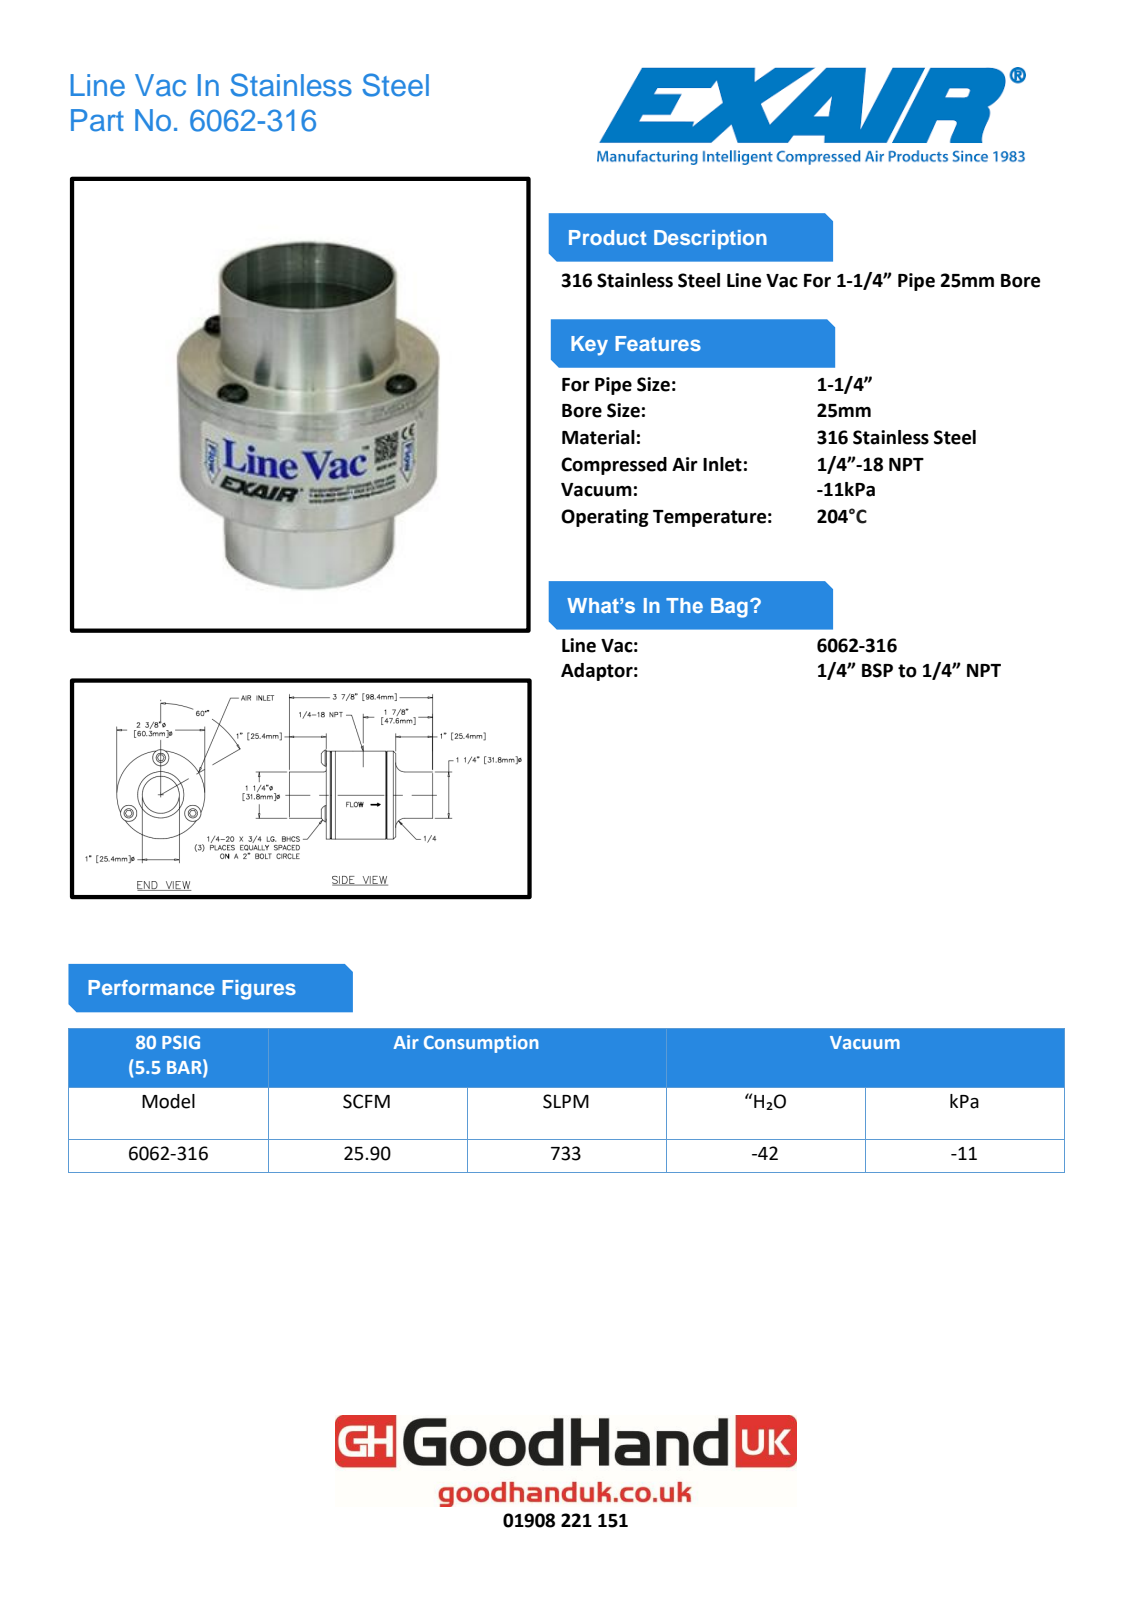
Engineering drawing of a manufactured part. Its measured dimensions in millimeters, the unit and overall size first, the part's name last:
Units: millimetres
Overall size (bounding box): 98.4 × 61.1 × 60.3
Round holes (diameter × count): ⌀5.2 ×3, ⌀6.4 ×3, ⌀7.1 ×3, ⌀11.1 ×1, ⌀25.4 ×1, ⌀41.9 ×1
Round bosses / shafts (diameter × count): ⌀60.3 ×1, ⌀60.3 ×1, ⌀31.8 ×1
Main face-to-face distances: 6.4, 9.5, 3.2, 47.6, 41.3, 38.1, 25.4, 73, 66.7, 63.5
Hole centre spacings: 44, 25.4, 25.4
Volume: 122 500 mm³ · Surface area: 35 650 mm²
Bodies: 5 solids, 84 faces (12 planar, 18 cylindrical, 54 other)
STEP written by: Autodesk Inventor 2010 (AUTOMOTIVE_DESIGN)
